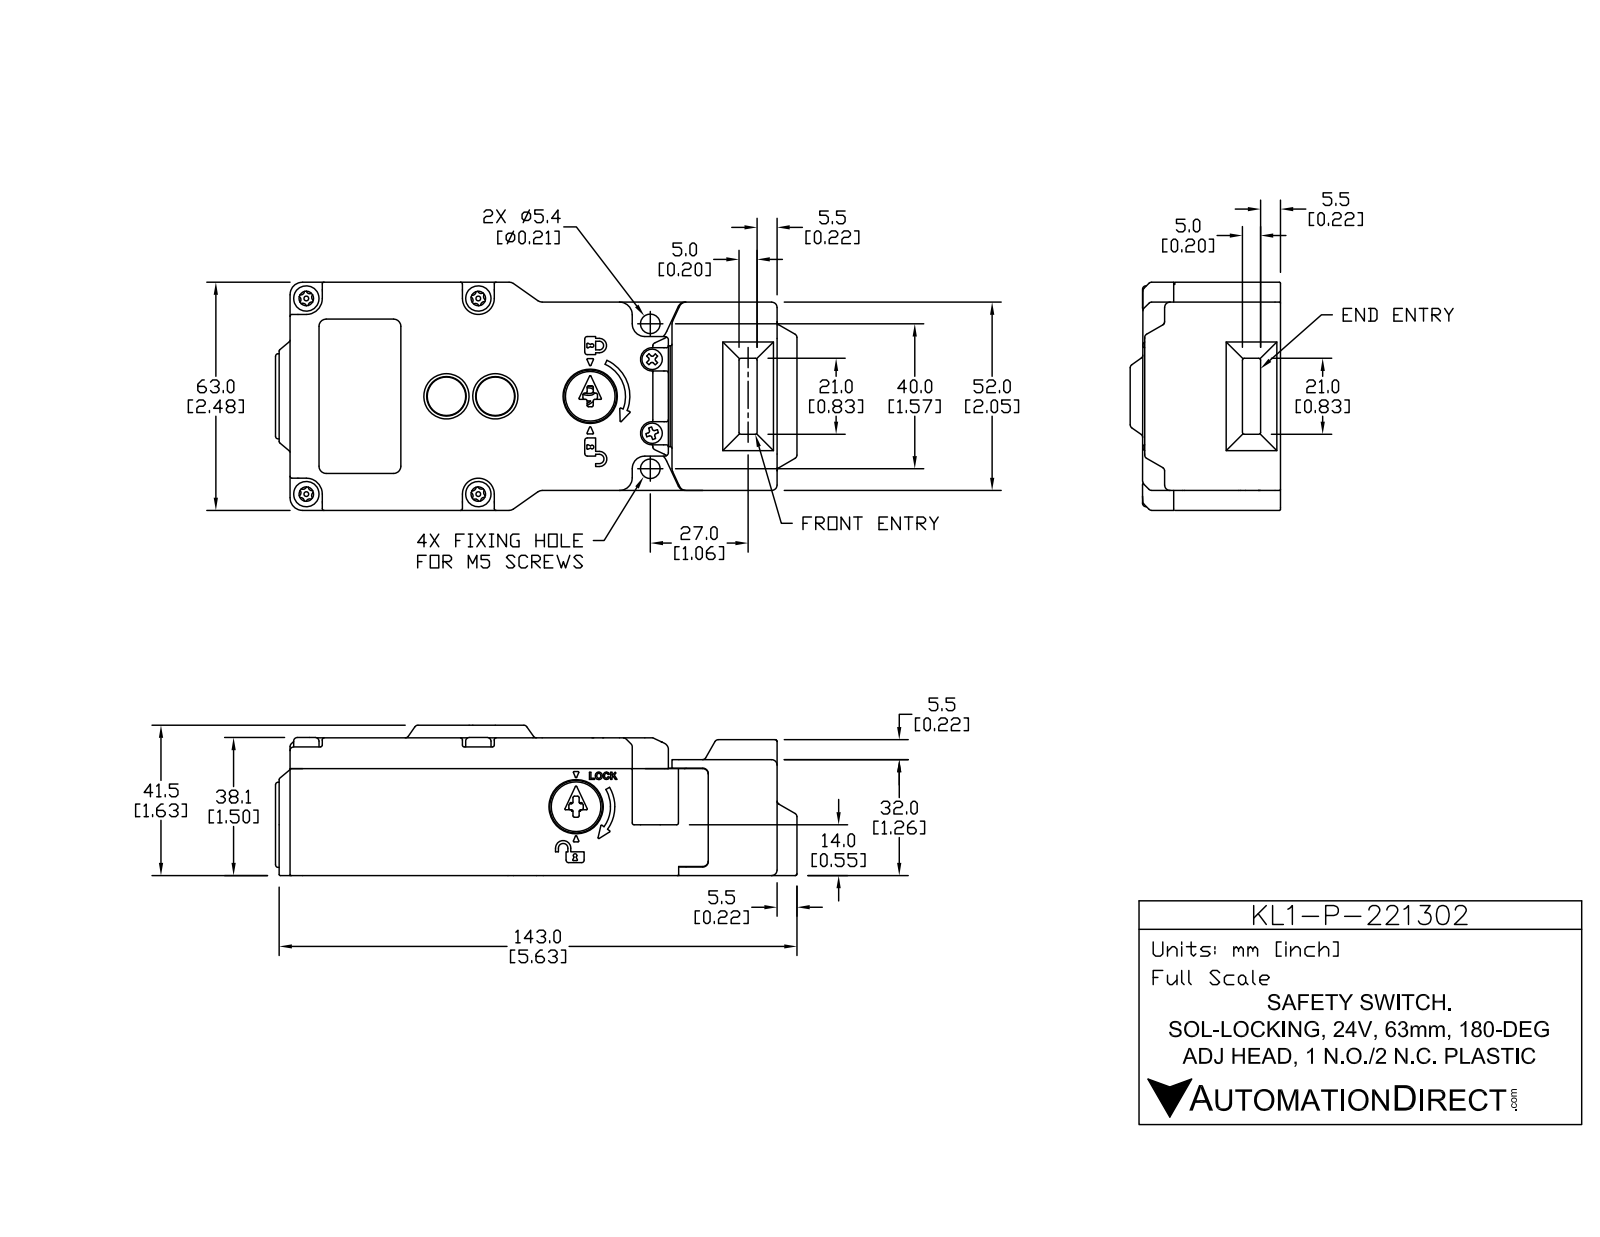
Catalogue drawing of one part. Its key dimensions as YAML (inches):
part_name: "KL1-P-221302"
step_written_by: "SolidWorks 2017 (AUTOMOTIVE_DESIGN)"
units: inches
bodies: {solids: 18, faces: 3047, planar: 909, cylindrical: 1225, other: 913}
overall_size: [5.669, 2.48, 1.634]
volume: 6.348
surface_area: 118.8
round_holes:
  - {diameter: 0.102, count: 4}
  - {diameter: 0.134, count: 4}
  - {diameter: 0.157, count: 4}
  - {diameter: 0.161, count: 4}
  - {diameter: 0.177, count: 4}
  - {diameter: 0.197, count: 4}
  - {diameter: 0.079, count: 2}
  - {diameter: 0.083, count: 2}
  - {diameter: 0.118, count: 2}
  - {diameter: 0.126, count: 2}
  - {diameter: 0.142, count: 2}
  - {diameter: 0.264, count: 2}
round_bosses_or_shafts:
  - {diameter: 0.276, count: 4}
  - {diameter: 0.138, count: 4}
  - {diameter: 0.051, count: 4}
  - {diameter: 0.197, count: 3}
  - {diameter: 0.039, count: 3}
  - {diameter: 0.571, count: 2}
  - {diameter: 0.417, count: 2}
  - {diameter: 0.362, count: 2}
partial_cylinders:
  - {radius: 0.02, count: 348}
  - {radius: 0.012, count: 126}
  - {radius: 0.039, count: 106}
  - {radius: 0.008, count: 30}
  - {radius: 0.016, count: 24}
  - {radius: 0.059, count: 16}
  - {radius: 0.006, count: 14}
  - {radius: 0.028, count: 12}
face_to_face_distances: [0.098, 0.118, 0.217, 1.496, 1.398, 1.402, 1.303, 0.094, 2.264, 2.146]
hole_center_spacings: [0.404, 0.498, 0.515, 0.549, 0.784, 0.803, 1.079, 1.118]
